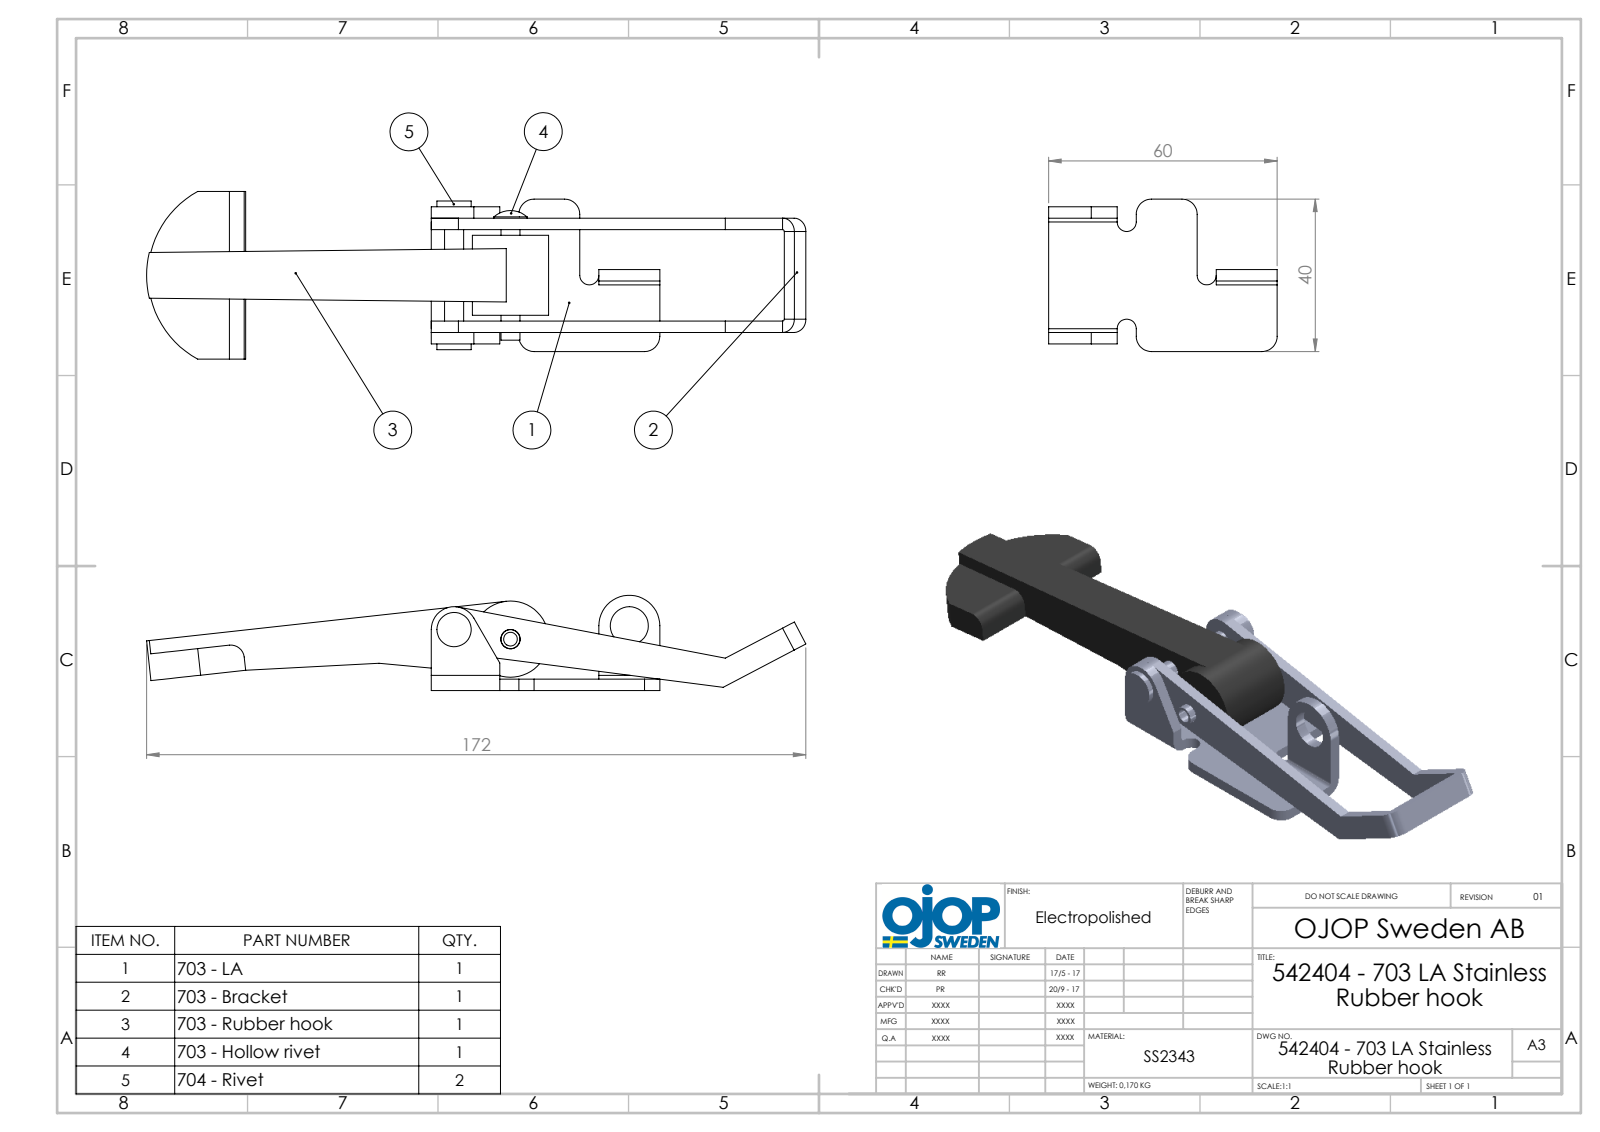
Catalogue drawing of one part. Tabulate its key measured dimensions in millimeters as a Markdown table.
| quantity | value |
| --- | --- |
| part name | 703 RF - Bygel; gummihake 703; 703 - Platta LA RF; 542404 - 703 LA Stainless Rubber hook (+2 more) |
| STEP written by | SolidWorks 2015 (AUTOMOTIVE_DESIGN) |
| units | millimeters |
| bodies | 6 solids, 143 faces (75 planar, 62 cylindrical, 6 other) |
| overall size | 173.07 × 44 × 25 |
| volume | 38 744 mm³ |
| surface area | 21 179 mm² |
| round holes (diameter × count) | 5.1 × 2, 2.5 × 1, 5.5 × 1, 7.2 × 1, 10 × 1 |
| round bosses / shafts (diameter × count) | 5 × 2, 20 × 1, 9 × 1, 7 × 1 |
| partial cylindrical surfaces (radius × count) | 4 × 7, 1 × 3, 2.5 × 3, 3.5 × 3, 0.5 × 2, 6 × 1, 8 × 1, 25 × 1 |
| main face-to-face distances | 3, 27, 30, 10.5, 16.5, 13.5, 24, 1.5, 4.5, 7.5 |
| hole center spacings | 15.01, 31.4, 46.01 |
